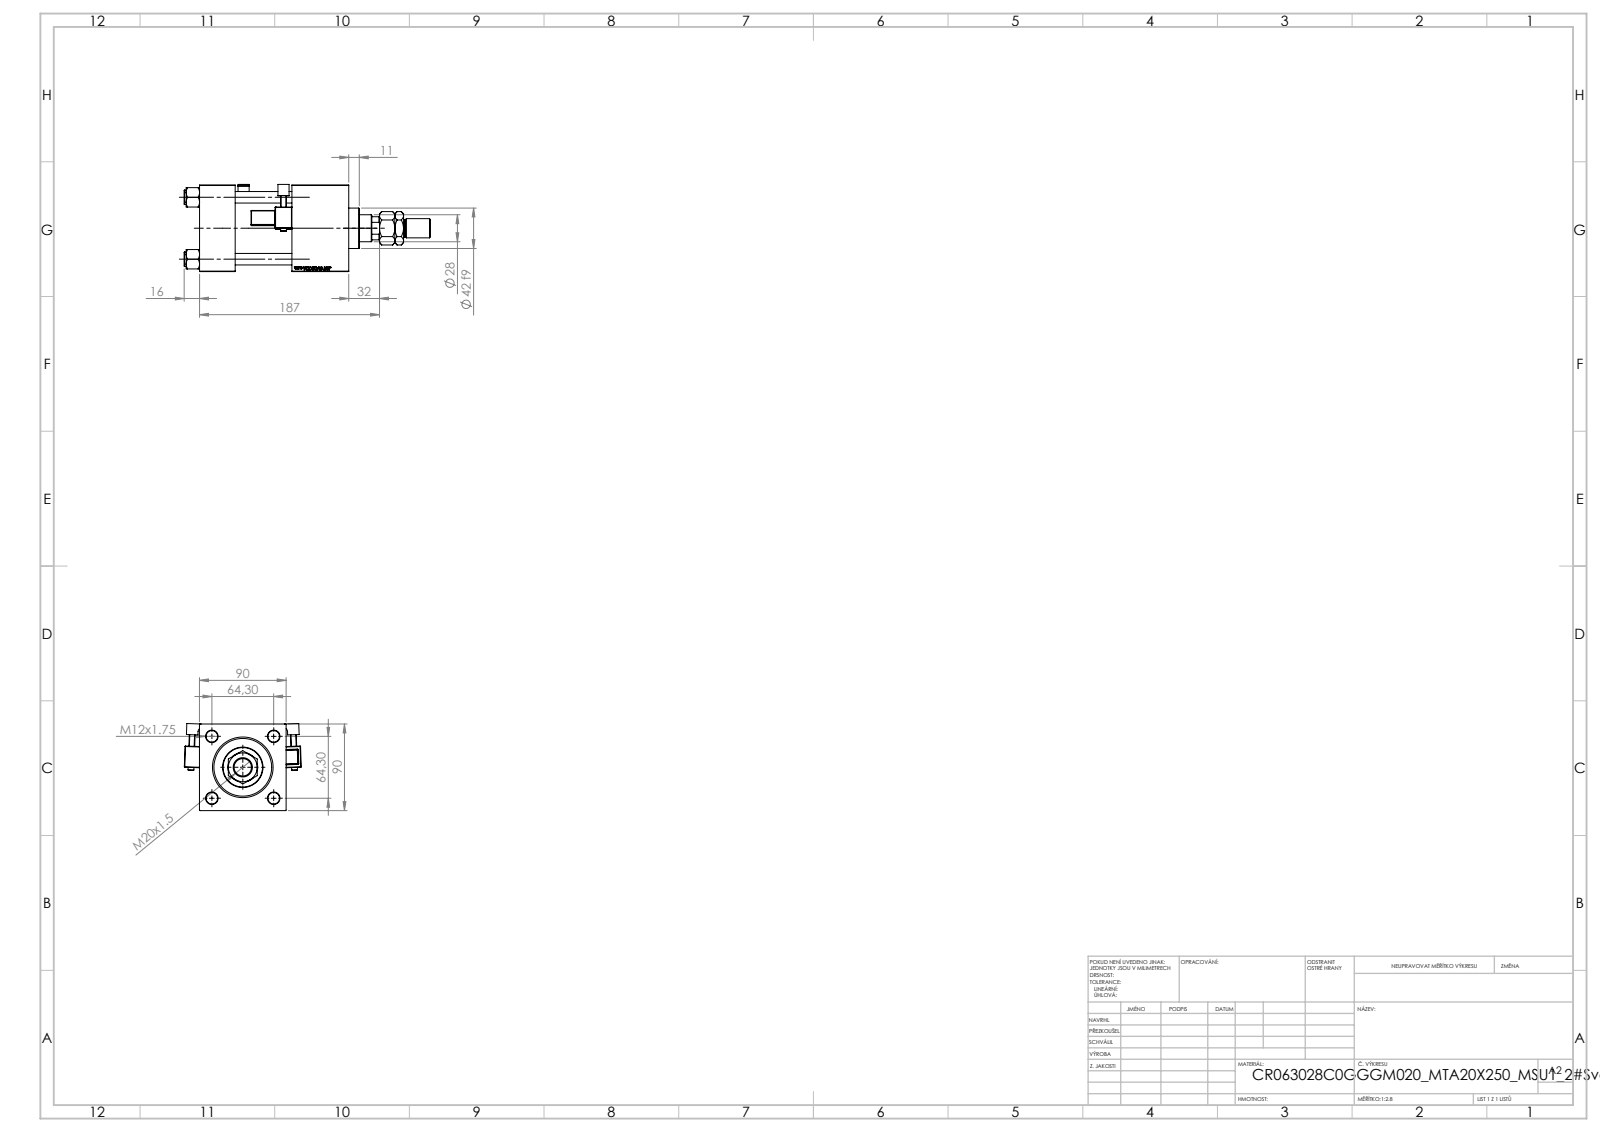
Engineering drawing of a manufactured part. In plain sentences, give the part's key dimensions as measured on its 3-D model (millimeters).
The part is named "V215CR_C_Body; NUT_M5_C; V215_VC_A; V215CR_VCP_C (+3 more)". Its 3-D file was written by "SolidWorks 2019 (CONFIG_CONTROL_DESIGN)". It is 14 solids with 1352 faces: 599 planar, 151 cylindrical and 602 other. Overall it measures 256 by 121.57 by 90.53 millimeters. Its volume is 1 016 000 cubic millimeters and its surface area 197 260 square millimeters. Round holes: 4 of diameter 12, 2 of diameter 7, 2 of diameter 20.96, 2 of diameter 30, 1 of diameter 18.5, 1 of diameter 28, 1 of diameter 31, 1 of diameter 50, 1 of diameter 60, 1 of diameter 63. Round bosses or shafts: 4 of diameter 15, 2 of diameter 6, 1 of diameter 69, 1 of diameter 42, 1 of diameter 20, 1 of diameter 18. Partial cylindrical surfaces (rounded edges, fillets, slot ends): 48 of radius 0.5, 2 of radius 1, 2 of radius 2.5, 2 of radius 4, 1 of radius 13.5. The main face-to-face distances are 90, 59, 37, 155, 118, 96, 126.3, 89.3, 30.3, 28.7. The hole center spacings are 45.47, 64.3, 90.93, 97.5.
